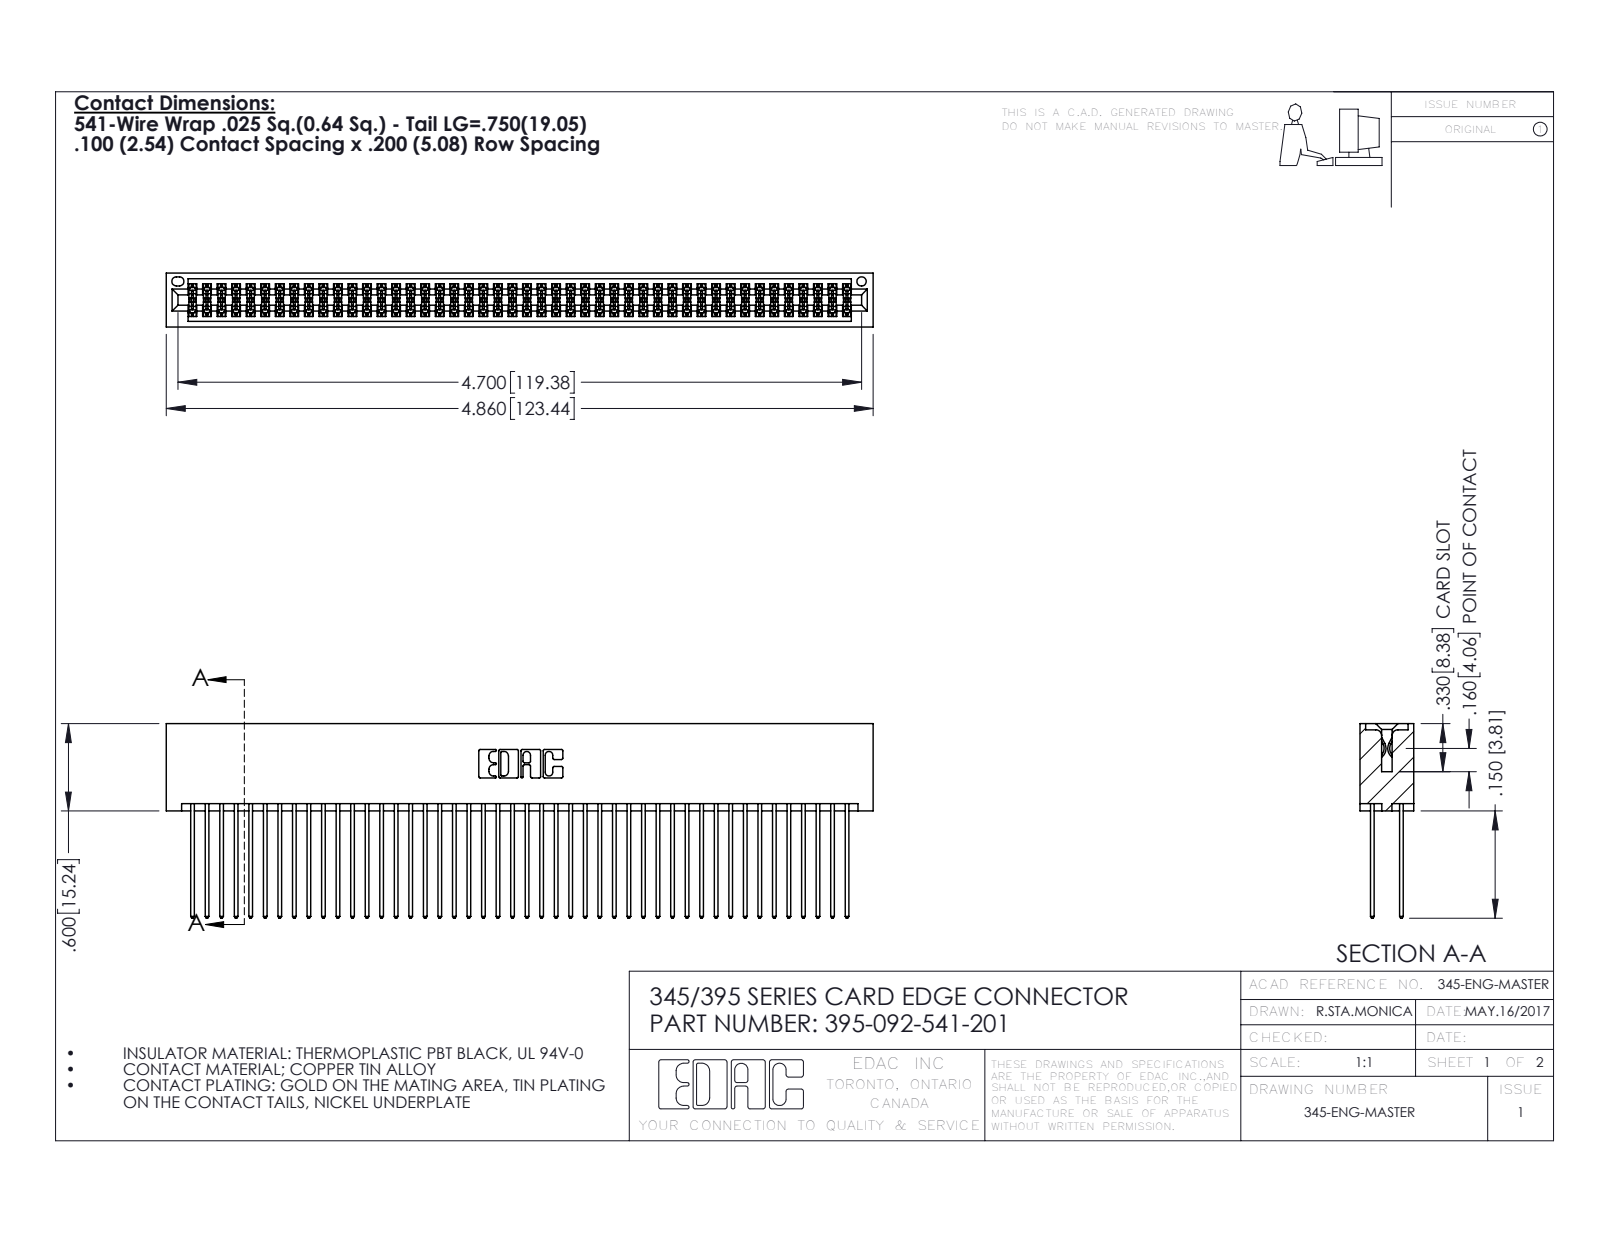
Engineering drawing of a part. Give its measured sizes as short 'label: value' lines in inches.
name: 395-092-541-201; 345 Part_No Mounting Lugs; 345-292-001_345-293-141
written by: SolidWorks 2016 (CONFIG_CONTROL_DESIGN)
unit: in
bodies: 93 solids, 4718 faces (3112 planar, 1606 cylindrical, 0 other)
size: 4.86 × 1.337 × 0.37
volume: 0.804 in³; area: 34.62 in²
holes: 1× ⌀0.064
rounds: 138× R0.006, 92× R0.01, 22× R0.01, 6× R0.007, 6× R0.031, 3× R0.026, 2× R0.014, 2× R0.019
face distances: 0.298, 0.072, 0.2, 0.098, 0.272, 0.025, 0.225, 0.37, 0.175, 0.149
